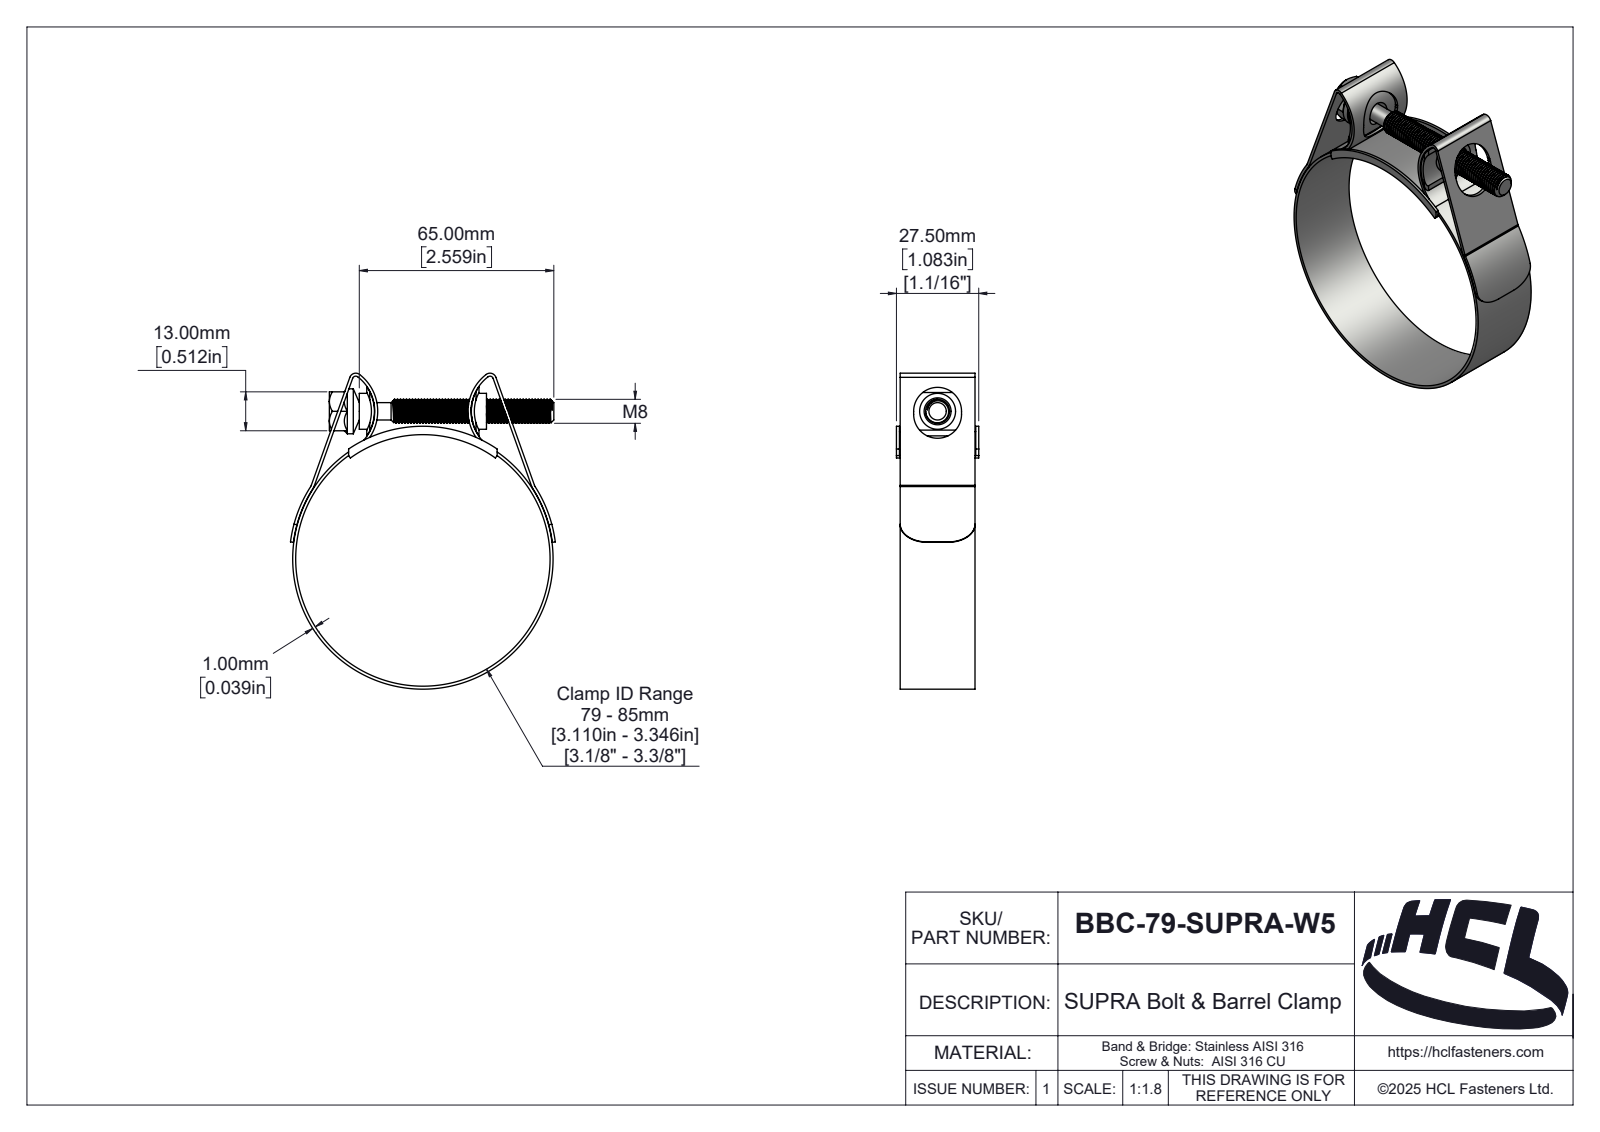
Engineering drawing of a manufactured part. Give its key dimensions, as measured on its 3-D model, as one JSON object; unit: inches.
{"part_name": "BBC-79-SUPRA-W5", "step_written_by": "SolidWorks 2025 (AUTOMOTIVE_DESIGN)", "units": "inches", "bodies": {"solids": 5, "faces": 349, "planar": 46, "cylindrical": 217, "other": 86}, "overall_size": [4.155, 3.483, 1.083], "volume_in3": 0.972, "surface_area_in2": 42.96, "round_holes": [[3.346, 1]], "round_bosses_or_shafts": [[3.425, 1], [0.591, 1], [0.472, 1], [0.315, 1], [0.228, 1]], "partial_cylinders_radius": [[0.039, 4], [0.043, 2], [0.079, 2], [0.083, 2], [0.118, 2], [0.315, 2], [0.529, 2], [0.568, 2]], "face_to_face_distances": [0.039, 0.984, 0.049, 1.033, 1.043, 0.994, 1.083, 0.512, 0.098, 1.575]}
